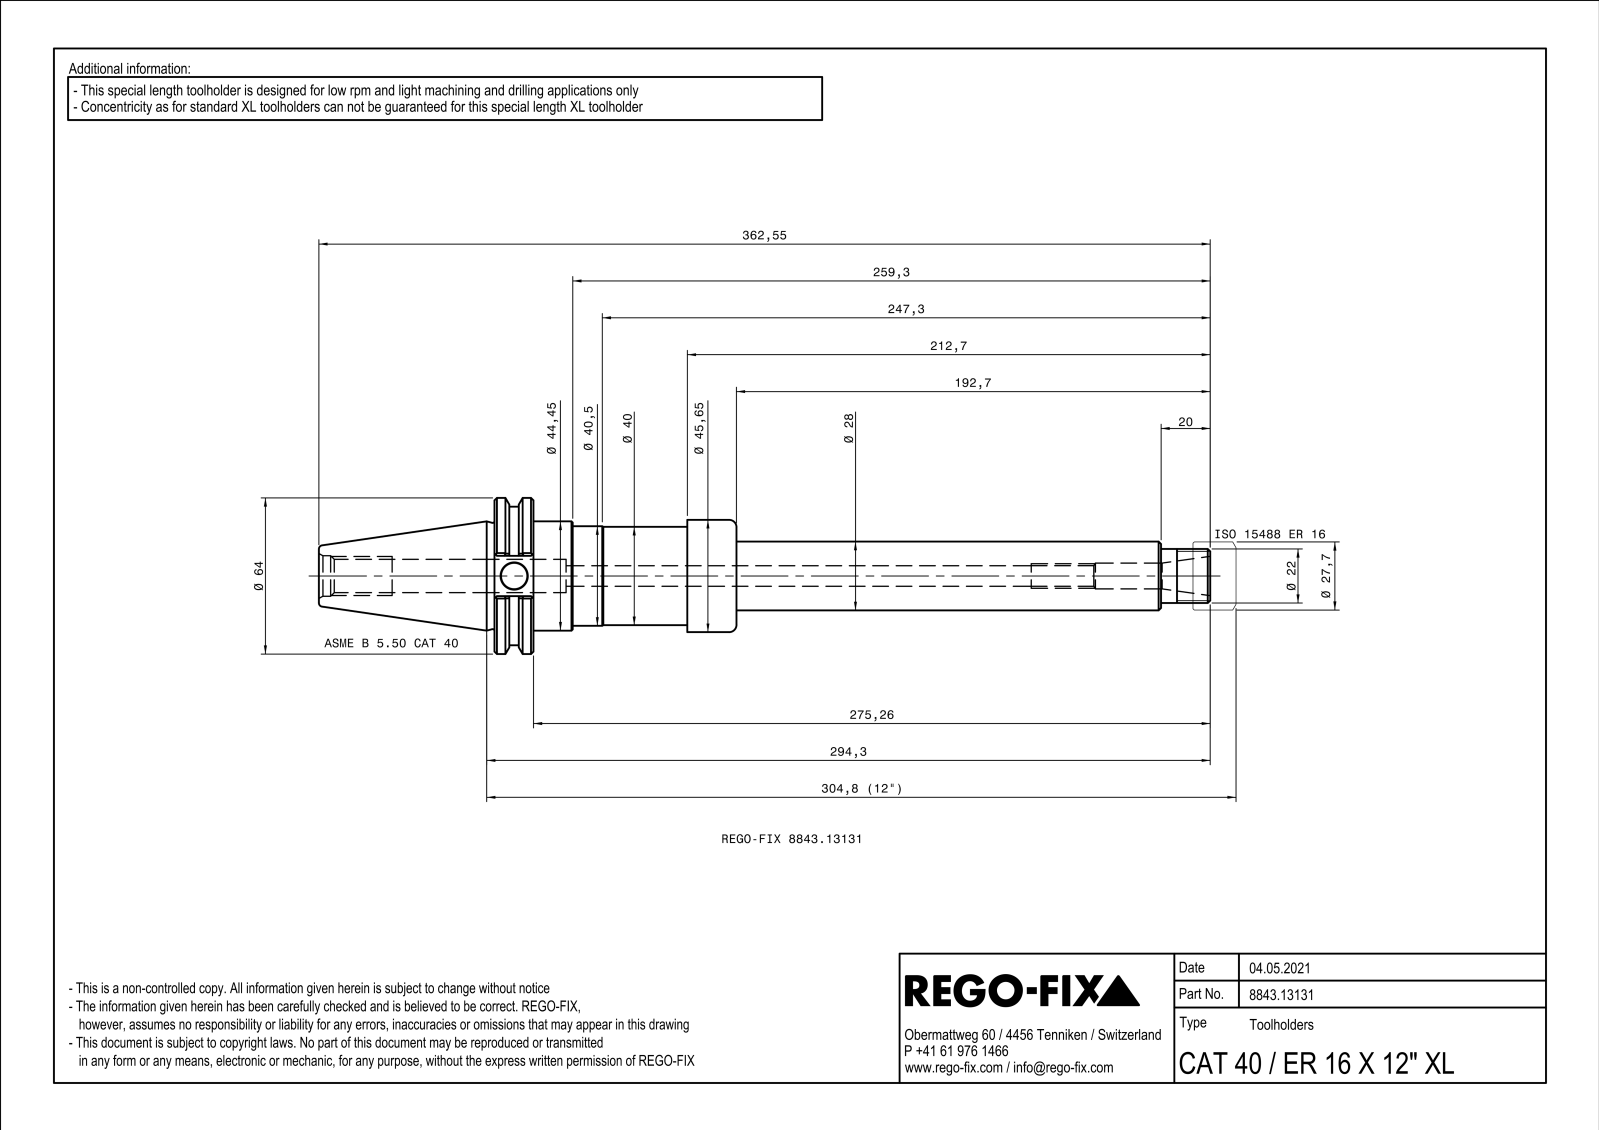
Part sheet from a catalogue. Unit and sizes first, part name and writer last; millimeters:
Units: millimetres
Overall size (bounding box): 362.55 × 63.5 × 60.79
Round holes (diameter × count): ⌀8.35 ×1, ⌀8.38 ×1, ⌀10 ×1, ⌀10.5 ×1, ⌀10.7 ×1, ⌀13.53 ×1, ⌀16.5 ×1, ⌀25 ×1, ⌀29 ×1, ⌀38.38 ×1, ⌀40.05 ×1, ⌀43.3 ×1
Round bosses / shafts (diameter × count): ⌀63.5 ×1, ⌀56.36 ×1, ⌀45.65 ×1, ⌀44.45 ×1, ⌀40.5 ×1, ⌀40 ×1, ⌀34 ×1, ⌀33 ×1
Partial cylindrical surfaces — rounded edges, fillets, slot ends (radius × count): R0.5 ×4
Main face-to-face distances: 15.87, 82.56, 98.43, 6, 14, 20, 1.5, 81.06, 96.93, 18.5
Volume: 300 844 mm³ · Surface area: 63 747 mm²
Bodies: 1 solid, 142 faces (42 planar, 32 cylindrical, 68 other)
Part name (STEP PRODUCT): NOCUT
STEP written by: SIEMENS PLM Software Solid Edge ST10 (AUTOMOTIVE_DESIGN)
